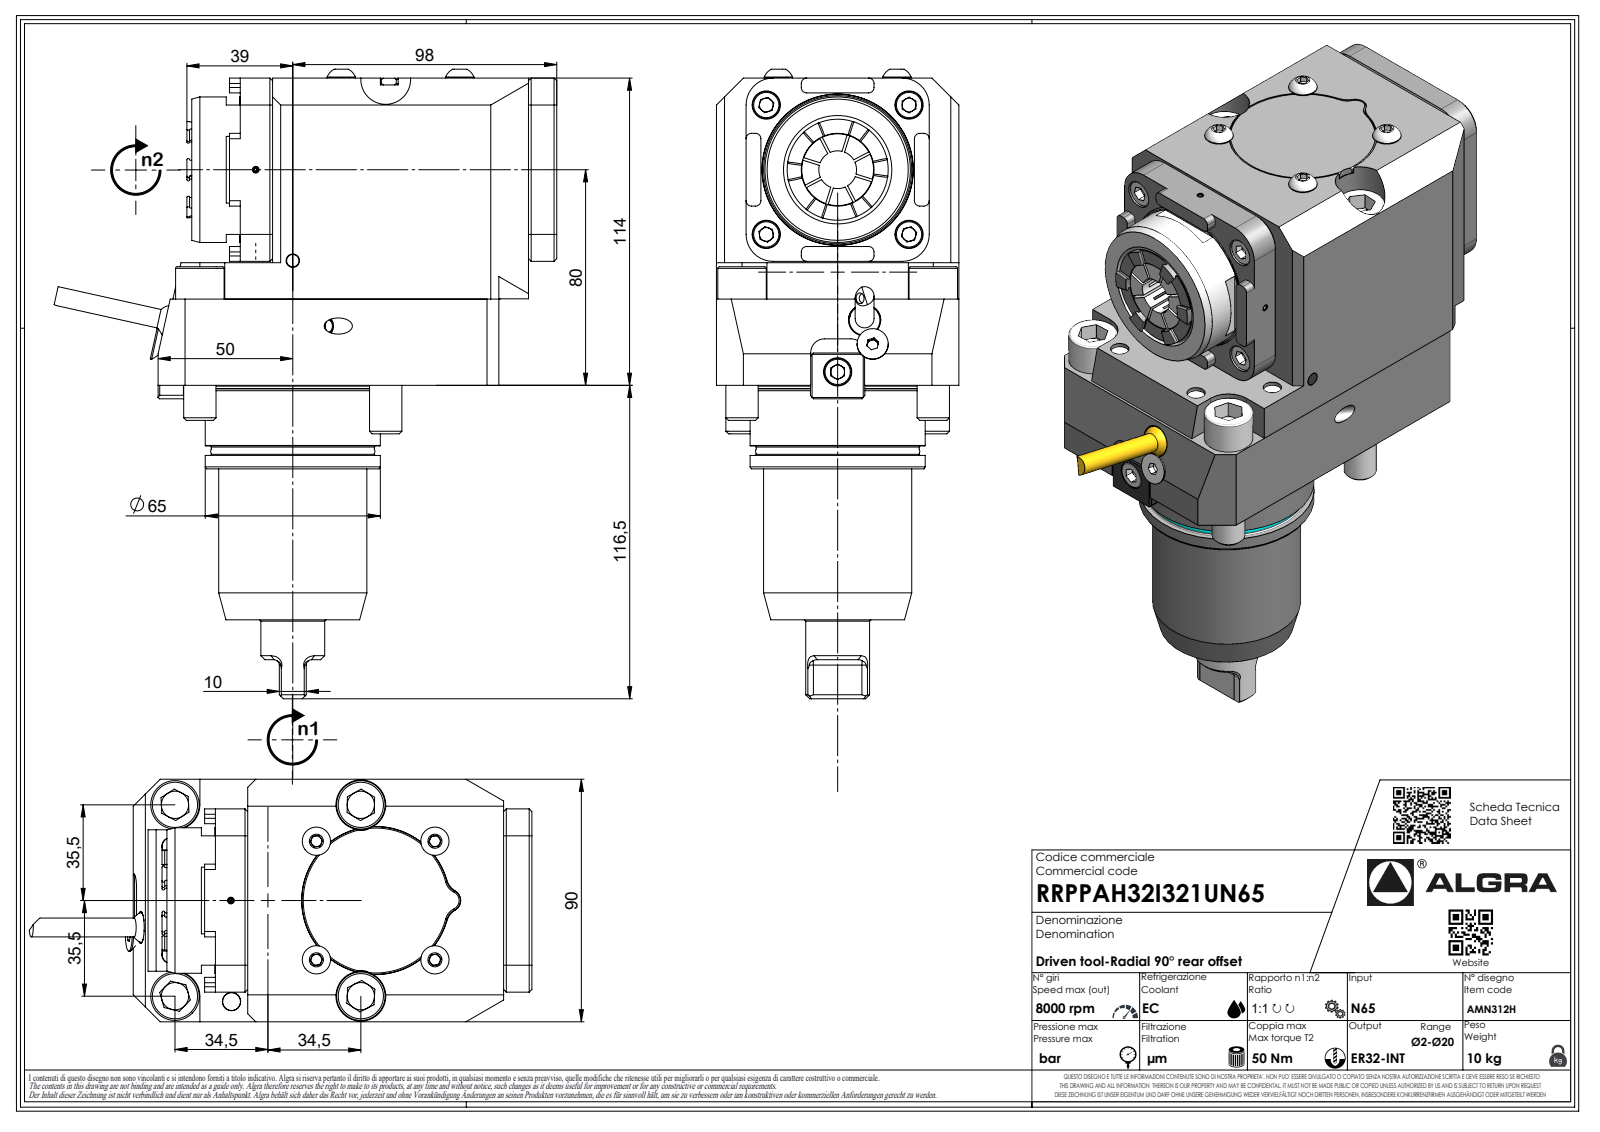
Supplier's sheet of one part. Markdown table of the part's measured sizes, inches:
| quantity | value |
| --- | --- |
| part name | RRPPAH32I321UN65 |
| STEP written by | SolidWorks 2023 (AUTOMOTIVE_DESIGN) |
| units | inches |
| bodies | 1 solid, 654 faces (370 planar, 117 cylindrical, 167 other) |
| overall size | 9.067 × 7.346 × 3.543 |
| volume | 89.7 in³ |
| surface area | 161.9 in² |
| round holes (diameter × count) | 0.728 × 2, 0.083 × 1, 0.157 × 1, 2.165 × 1 |
| round bosses / shafts (diameter × count) | 0.709 × 4, 0.472 × 4, 2.559 × 1, 2.543 × 1, 2.382 × 1, 2.165 × 1, 2.157 × 1, 2.126 × 1 |
| partial cylindrical surfaces (radius × count) | 0.079 × 23, 0.013 × 7, 0.02 × 7, 0.146 × 7, 0.197 × 4, 0.394 × 4, 0.157 × 2, 0.201 × 2 |
| main face-to-face distances | 3.543, 4.488, 0.433, 2.697, 1.791, 0.846, 2.677, 4.486, 2.695, 3.11 |
| hole center spacings | 1.414, 2.795 |
